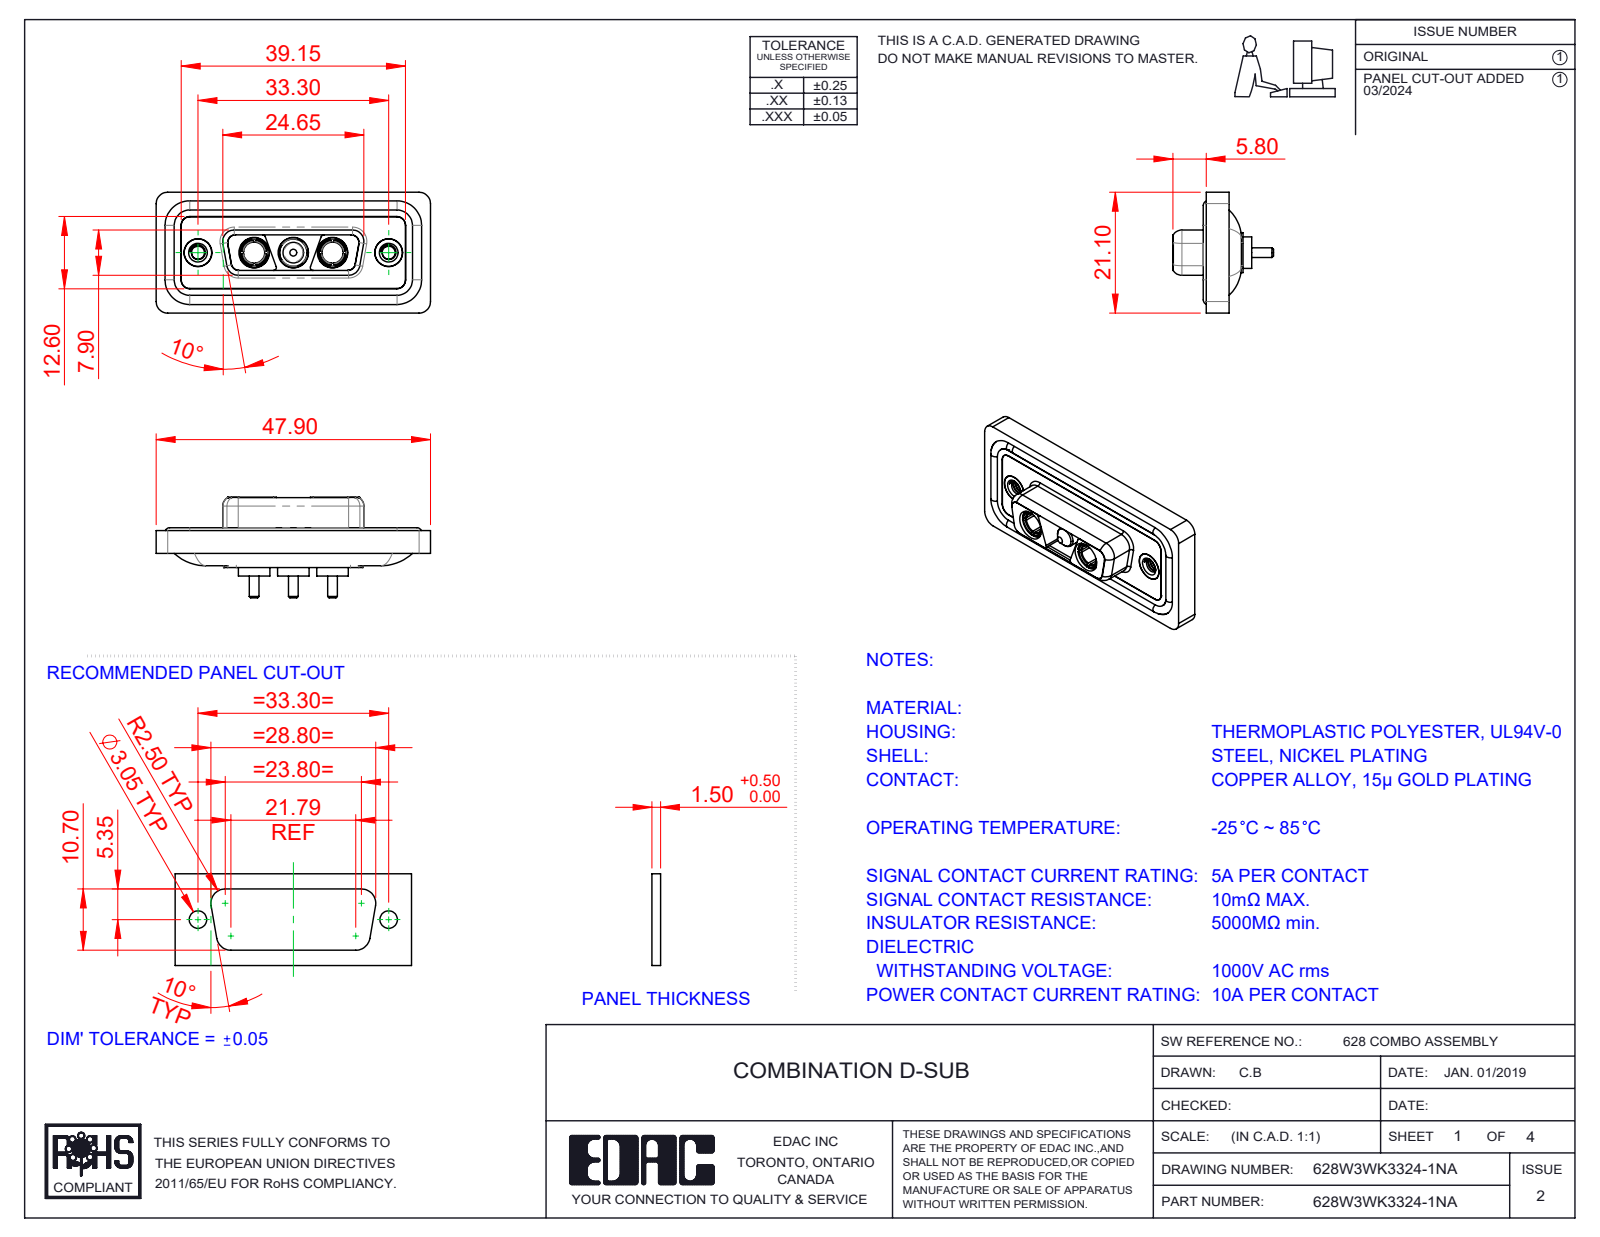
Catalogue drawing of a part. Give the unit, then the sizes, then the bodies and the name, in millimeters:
Units: millimetres
Overall size (bounding box): 47.9 × 21.1 × 17.55
Round holes (diameter × count): ⌀4.85 ×5, ⌀5.3 ×3, ⌀2.26 ×2, ⌀3.7 ×2, ⌀4 ×2, ⌀4.05 ×2, ⌀5 ×2
Round bosses / shafts (diameter × count): ⌀1.6 ×4, ⌀5.5 ×3, ⌀5.2 ×3, ⌀4.75 ×3, ⌀3.75 ×3, ⌀1.7 ×3, ⌀4.96 ×2, ⌀4.95 ×2
Partial cylindrical surfaces — rounded edges, fillets, slot ends (radius × count): R1.5 ×22, R2 ×20, R1.35 ×12, R0.5 ×8, R1.6 ×8, R0.25 ×4, R0.6 ×4, R0.65 ×4
Main face-to-face distances: 0.4, 1.6, 1.8, 0.5, 1.1, 2.9, 5.65, 7.05, 1.5, 5.35
Hole centre spacings: 6.85, 9.8, 16.65, 23.5, 13.7, 33.3
Volume: 5 836 mm³ · Surface area: 9 464 mm²
Bodies: 13 solids, 581 faces (178 planar, 260 cylindrical, 143 other)
Part name (STEP PRODUCT): 628Combo Waterproof Housing_15 Contacts; Power Pin_10A S; 628Combo Housing_3WK3; 628Combo Threaded Rivet_A (+4 more)
STEP written by: SolidWorks 2023 (CONFIG_CONTROL_DESIGN)
